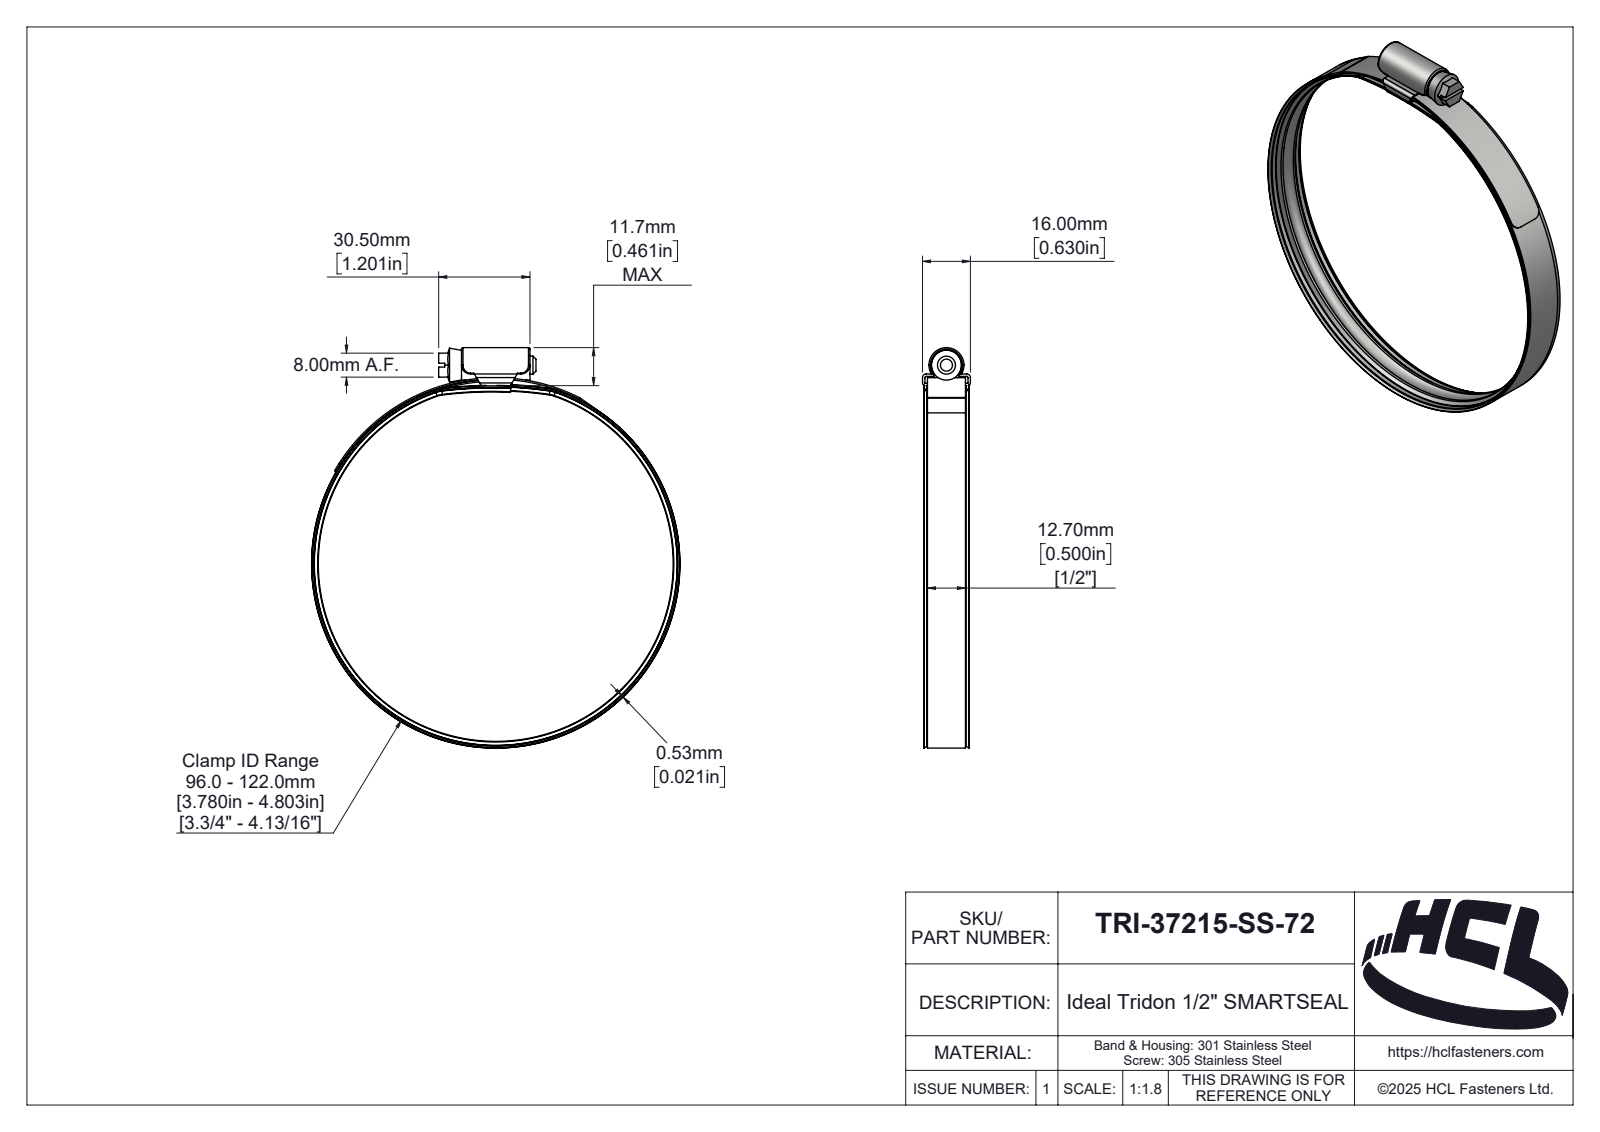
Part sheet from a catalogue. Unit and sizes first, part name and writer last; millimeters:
Units: millimetres
Overall size (bounding box): 133.73 × 123.06 × 16
Round holes (diameter × count): ⌀121.4 ×1, ⌀122 ×1
Round bosses / shafts (diameter × count): ⌀123.06 ×1, ⌀121.8 ×1, ⌀10 ×1, ⌀6 ×1
Partial cylindrical surfaces — rounded edges, fillets, slot ends (radius × count): R0.5 ×6, R3 ×4, R0.1 ×2, R0.9 ×2, R1.2 ×2, R9.9 ×2, R10.1 ×2, R0.46 ×1
Main face-to-face distances: 12.7, 0.8, 3.1, 0.53, 2.3, 30.5, 3.9, 1.65, 14.35, 15.2
Volume: 7 402 mm³ · Surface area: 28 210 mm²
Bodies: 4 solids, 418 faces (42 planar, 119 cylindrical, 257 other)
Part name (STEP PRODUCT): TRI-37215-SS-72
STEP written by: SolidWorks 2025 (AUTOMOTIVE_DESIGN)
